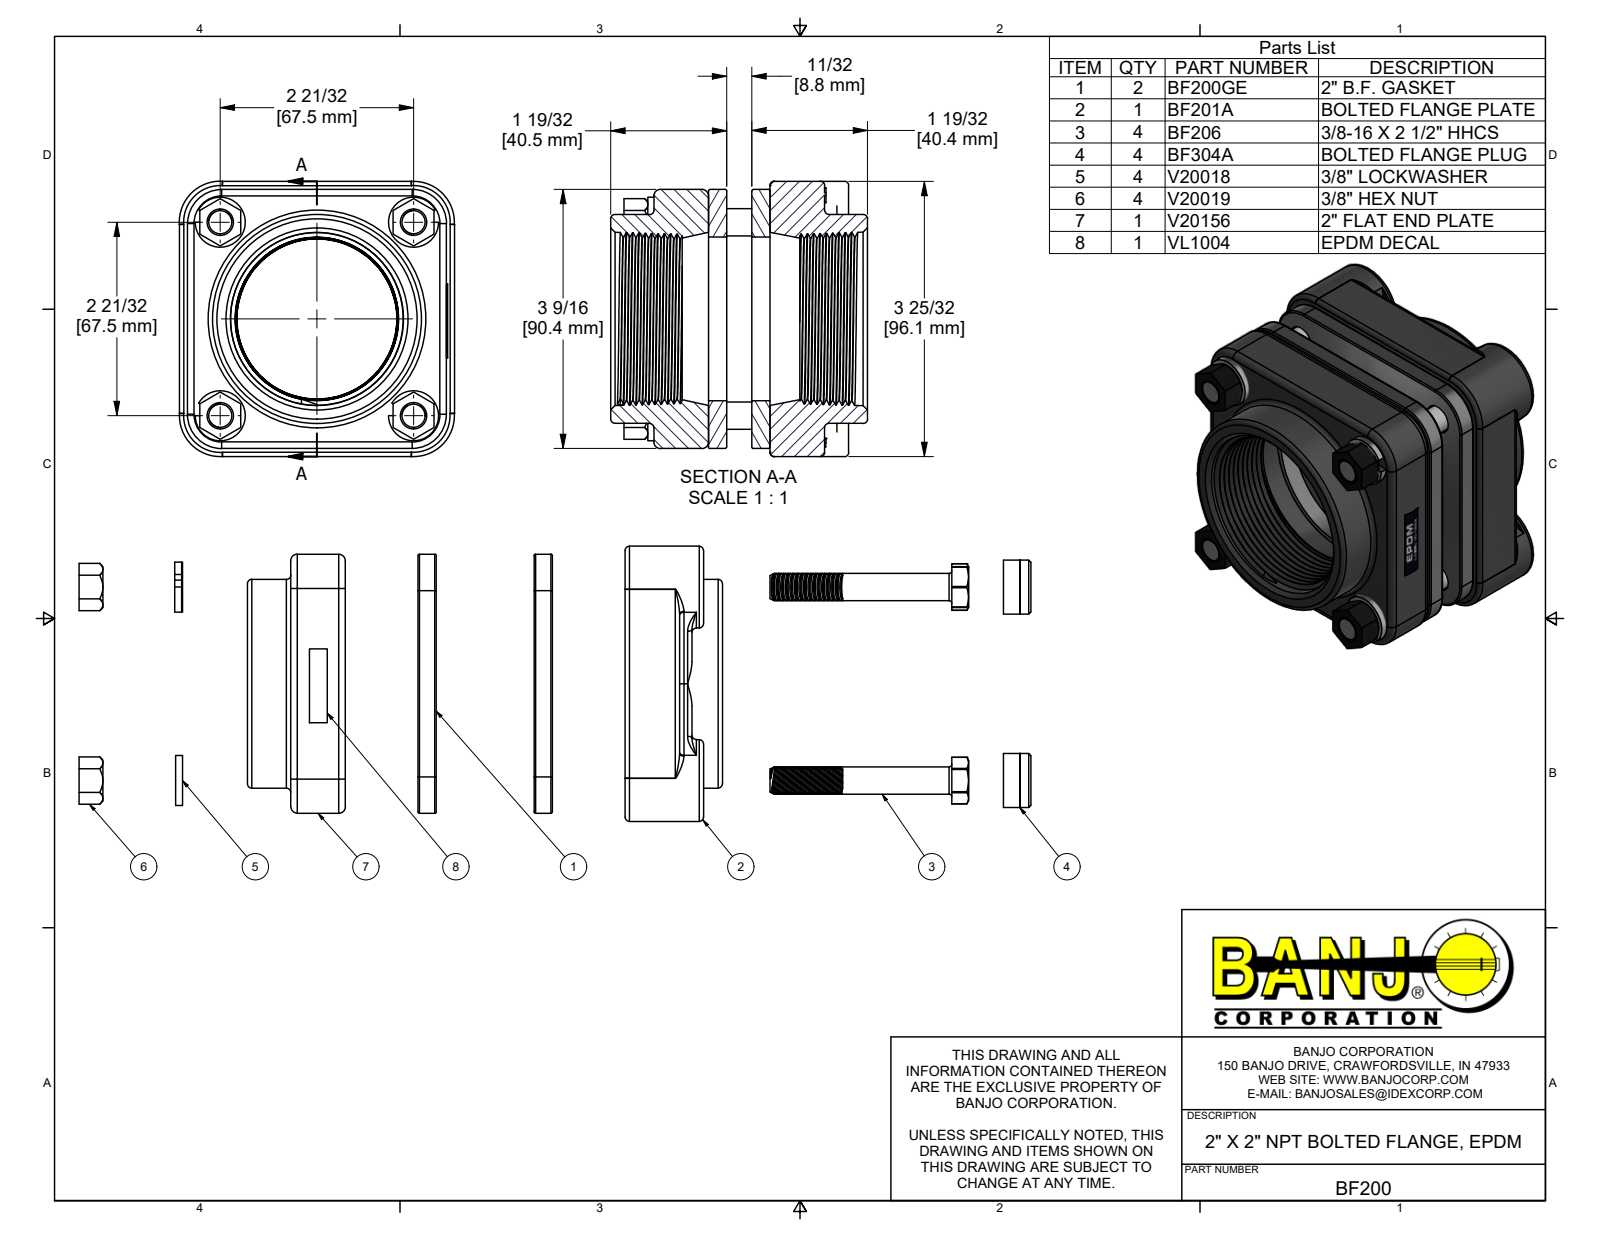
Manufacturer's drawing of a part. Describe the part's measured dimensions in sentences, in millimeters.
The part is named "BF200; V20019; BF201A; V20156 (+5 more)". Its 3-D file was written by "Autodesk Inventor 2019 (AUTOMOTIVE_DESIGN)". It is 21 solids with 1128 faces: 319 planar, 346 cylindrical and 463 other. Overall it measures 974.1 by 96.1 by 96.1 millimeters. Its volume is 365 800 cubic millimeters and its surface area 296 500 square millimeters. Round holes: 4 of diameter 7.8, 4 of diameter 9.7, 4 of diameter 9.8, 4 of diameter 10.3, 4 of diameter 10.4, 4 of diameter 18.2, 4 of diameter 19.1, 1 of diameter 57.2. Round bosses or shafts: 60 of diameter 8.2, 4 of diameter 28.6, 4 of diameter 18.8, 4 of diameter 17.4, 4 of diameter 9.5, 1 of diameter 72.9. Partial cylindrical surfaces (rounded edges, fillets, slot ends): 16 of radius 0.5, 16 of radius 1.5, 8 of radius 2.3, 8 of radius 4.1, 4 of radius 8.1, 4 of radius 11.9, 4 of radius 12.7, 4 of radius 40.6. The main face-to-face distances are 6.4, 15.2, 21.5, 8.8, 2.8, 93.2, 19.1, 25.4, 34.2, 40.6. The hole center spacings are 47.8, 67.5, 95.5.
